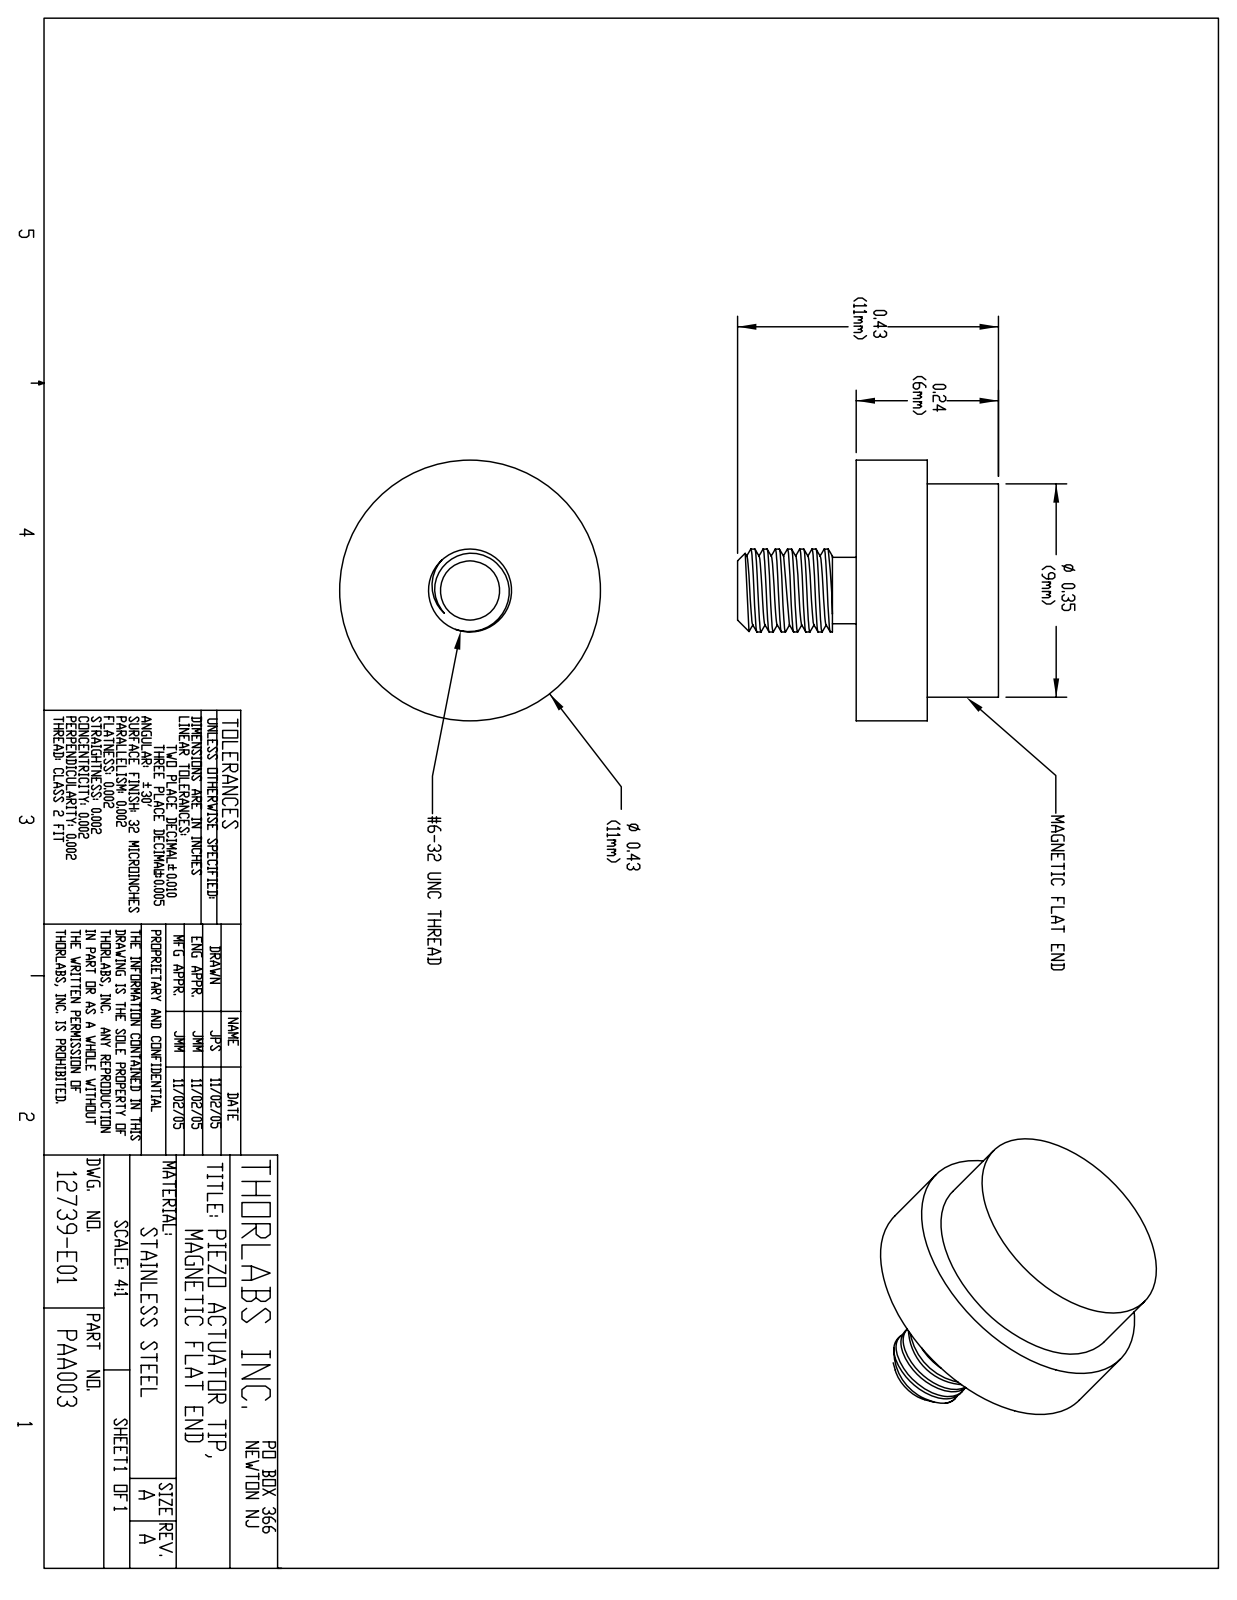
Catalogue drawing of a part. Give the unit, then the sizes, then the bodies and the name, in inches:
Units: inches
Overall size (bounding box): 0.433 × 0.433 × 0.433
Round bosses / shafts (diameter × count): ⌀0.433 ×1, ⌀0.354 ×1, ⌀0.138 ×1, ⌀0.11 ×1
Main face-to-face distances: 0.118, 0.236, 0.433, 0.315, 0.197
Bodies: 0 solids, 29 faces (4 planar, 21 cylindrical, 4 other)
Part name (STEP PRODUCT): 12739-E0W
STEP written by: SolidWorks 2007 (AUTOMOTIVE_DESIGN)
